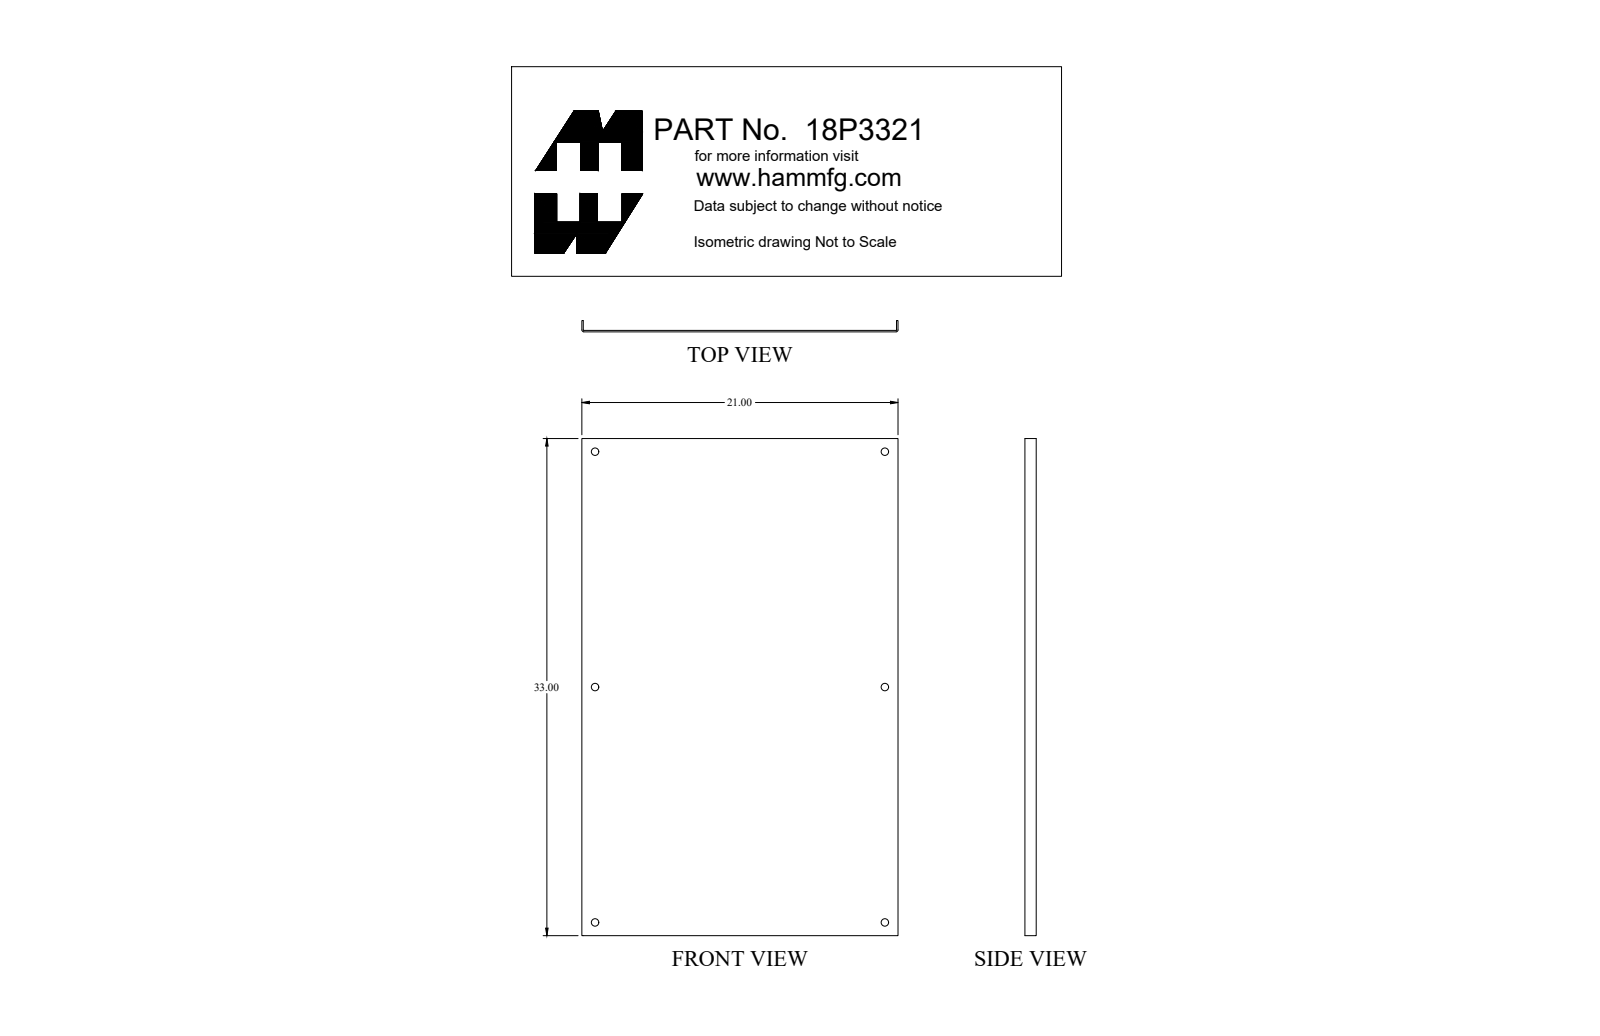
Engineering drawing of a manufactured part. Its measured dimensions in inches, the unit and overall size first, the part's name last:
Units: inches
Overall size (bounding box): 33 × 21 × 0.75
Round holes (diameter × count): ⌀0.5 ×6
Partial cylindrical surfaces — rounded edges, fillets, slot ends (radius × count): R0.03 ×2, R0.125 ×2
Main face-to-face distances: 0.095, 20.905, 21, 20.81, 0.75, 0.655, 33
Hole centre spacings: 15.625, 24.793, 19.25, 31.25, 36.703
Volume: 69.62 in³ · Surface area: 1 477 in²
Bodies: 1 solid, 26 faces (10 planar, 16 cylindrical, 0 other)
Part name (STEP PRODUCT): 18P3321_Default
STEP written by: SolidWorks 2018 (CONFIG_CONTROL_DESIGN)
